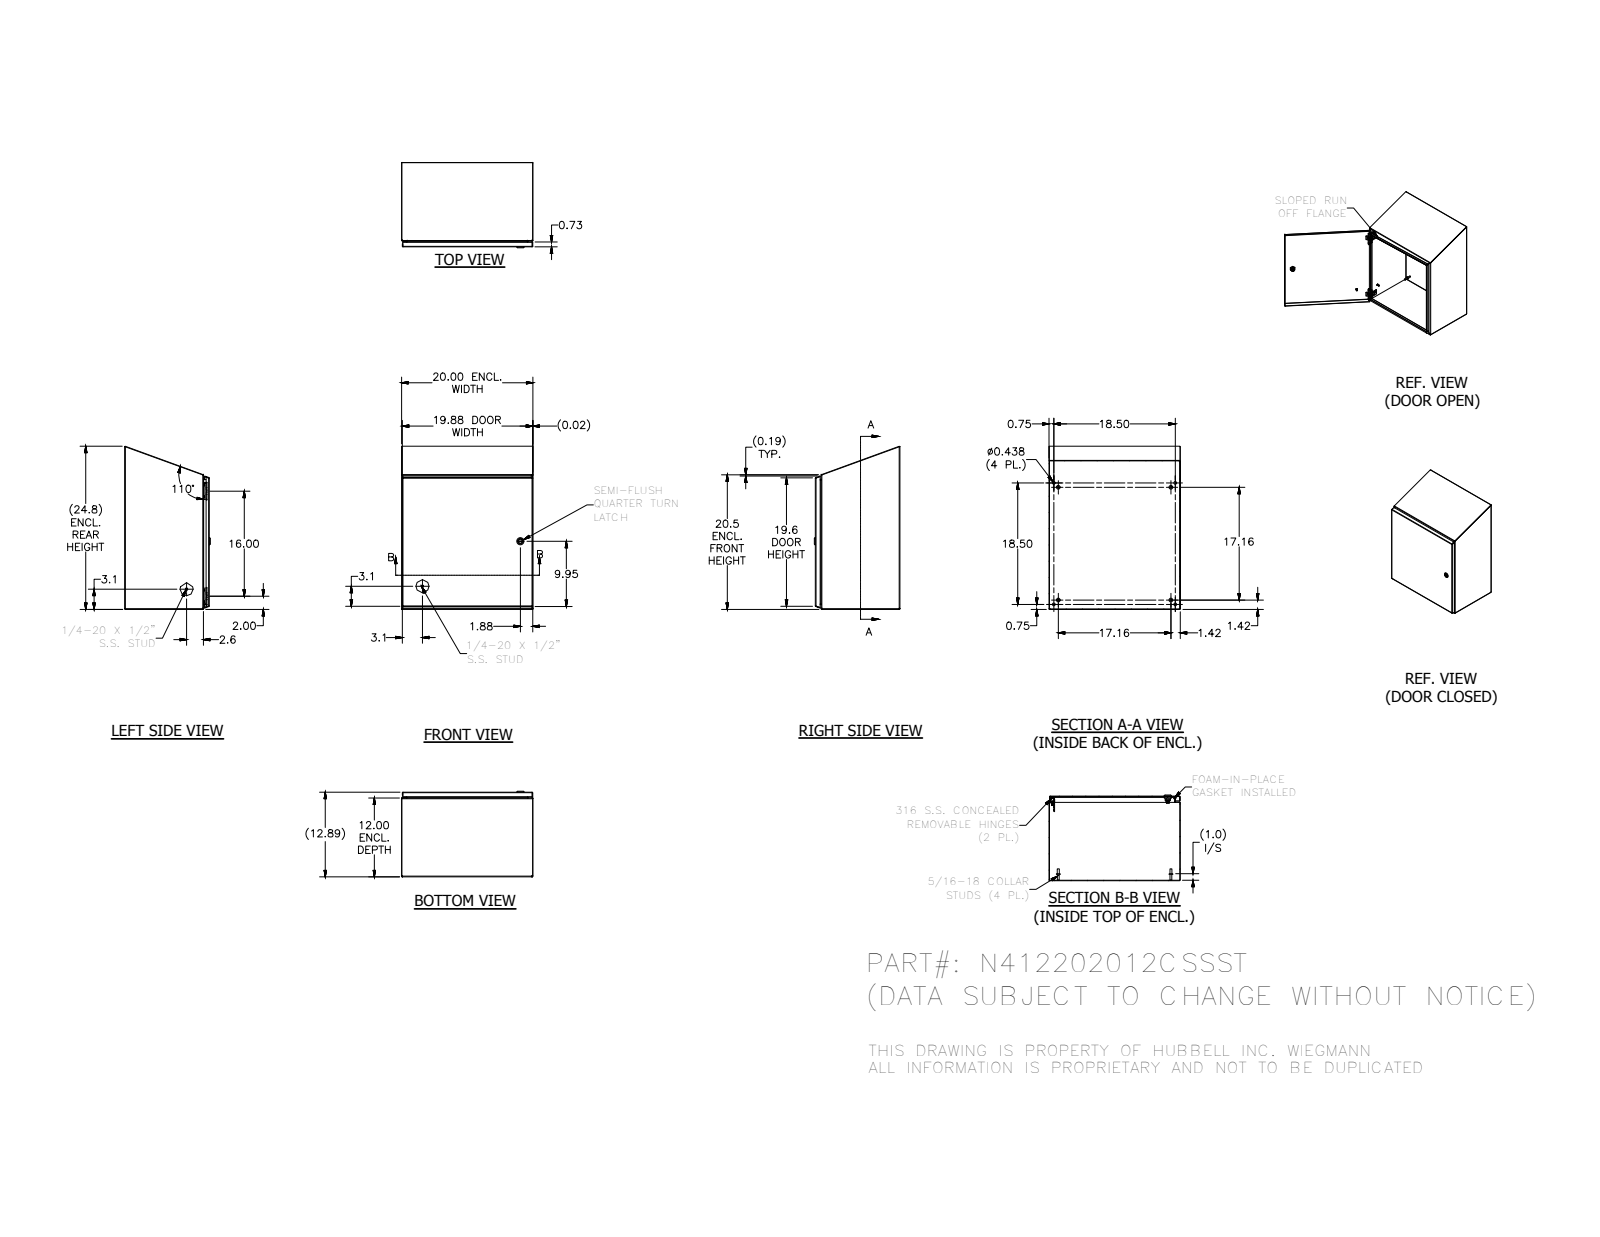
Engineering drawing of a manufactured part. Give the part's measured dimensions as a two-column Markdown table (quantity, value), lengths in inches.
| quantity | value |
| --- | --- |
| part name | N412202012CSSST |
| STEP written by | SolidWorks 2018 (AUTOMOTIVE_DESIGN) |
| units | inches |
| bodies | 36 solids, 1426 faces (538 planar, 509 cylindrical, 379 other) |
| overall size | 24.847 × 20 × 13.044 |
| volume | 155.6 in³ |
| surface area | 4 231 in² |
| round holes (diameter × count) | 0.093 × 4, 0.152 × 4, 0.167 × 4, 0.172 × 4, 0.187 × 4, 0.437 × 4, 0.156 × 3, 0.187 × 1, 0.197 × 1, 0.315 × 1, 0.394 × 1, 0.402 × 1 |
| round bosses / shafts (diameter × count) | 0.25 × 10, 0.563 × 4, 0.36 × 4, 0.32 × 4, 0.3 × 4, 0.275 × 4, 0.256 × 4, 0.164 × 4 |
| partial cylindrical surfaces (radius × count) | 0.031 × 29, 0.05 × 26, 0.105 × 19, 0.016 × 18, 0.02 × 16, 0.125 × 16, 0.032 × 8, 0.524 × 6 |
| main face-to-face distances | 0.074, 12.813, 19.926, 12.739, 12.887, 19.852, 20, 11.926, 0.887, 0.813 |
| hole center spacings | 16, 18.5, 0.5, 0.656, 0.66, 0.952, 1.307, 1.311 |
